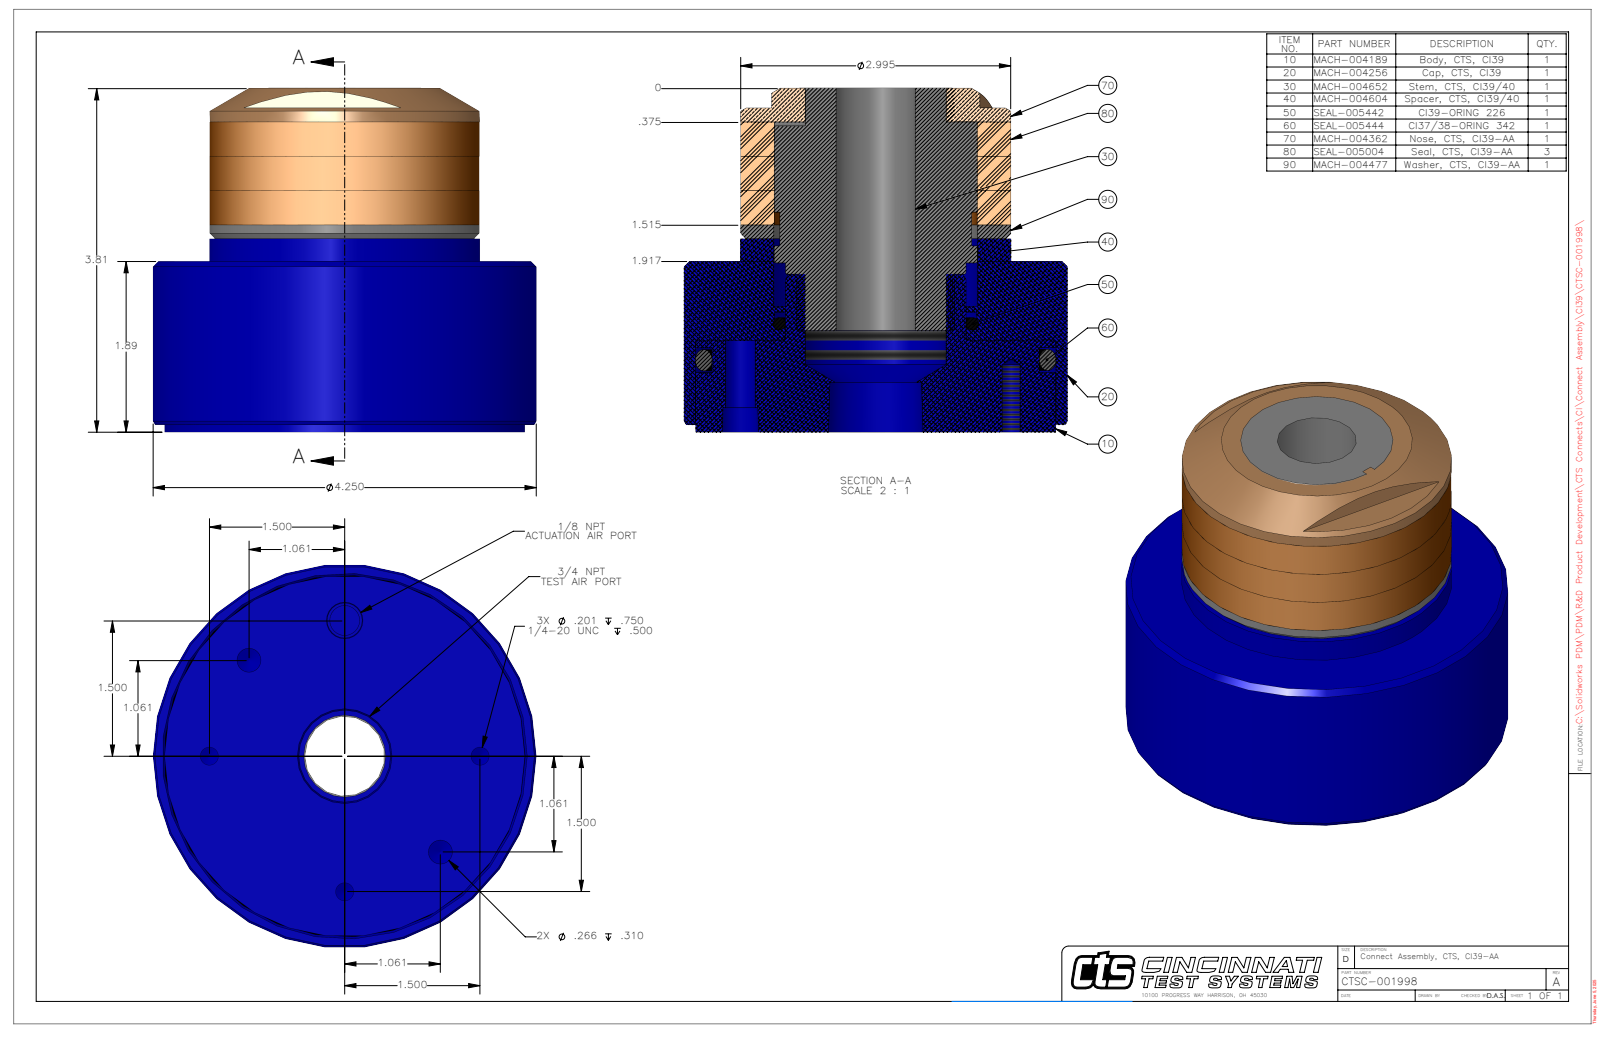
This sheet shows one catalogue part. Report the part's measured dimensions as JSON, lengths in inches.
{"part_name": "CTSC-001998", "step_written_by": "SolidWorks 2023 (AUTOMOTIVE_DESIGN)", "units": "inches", "bodies": {"solids": 1, "faces": 94, "planar": 32, "cylindrical": 39, "other": 23}, "overall_size": [4.25, 4.25, 3.813], "volume_in3": 36.99, "surface_area_in2": 101.2, "round_holes": [[0.201, 3], [0.266, 2], [0.332, 1], [0.88, 1], [2.25, 1], [2.26, 1], [2.261, 1], [4, 1]], "round_bosses_or_shafts": [[4.25, 1], [3.992, 1], [3, 1], [2.995, 1], [2.12, 1]], "partial_cylinders_radius": [[0.062, 1], [0.781, 1]], "face_to_face_distances": [1.893, 3.813, 1.92, 3.81, 1.917, 0.083, 1.81, 3.727, 3.73, 3.591], "hole_center_spacings": [1.5, 1.148, 2.121, 2.772, 3]}
